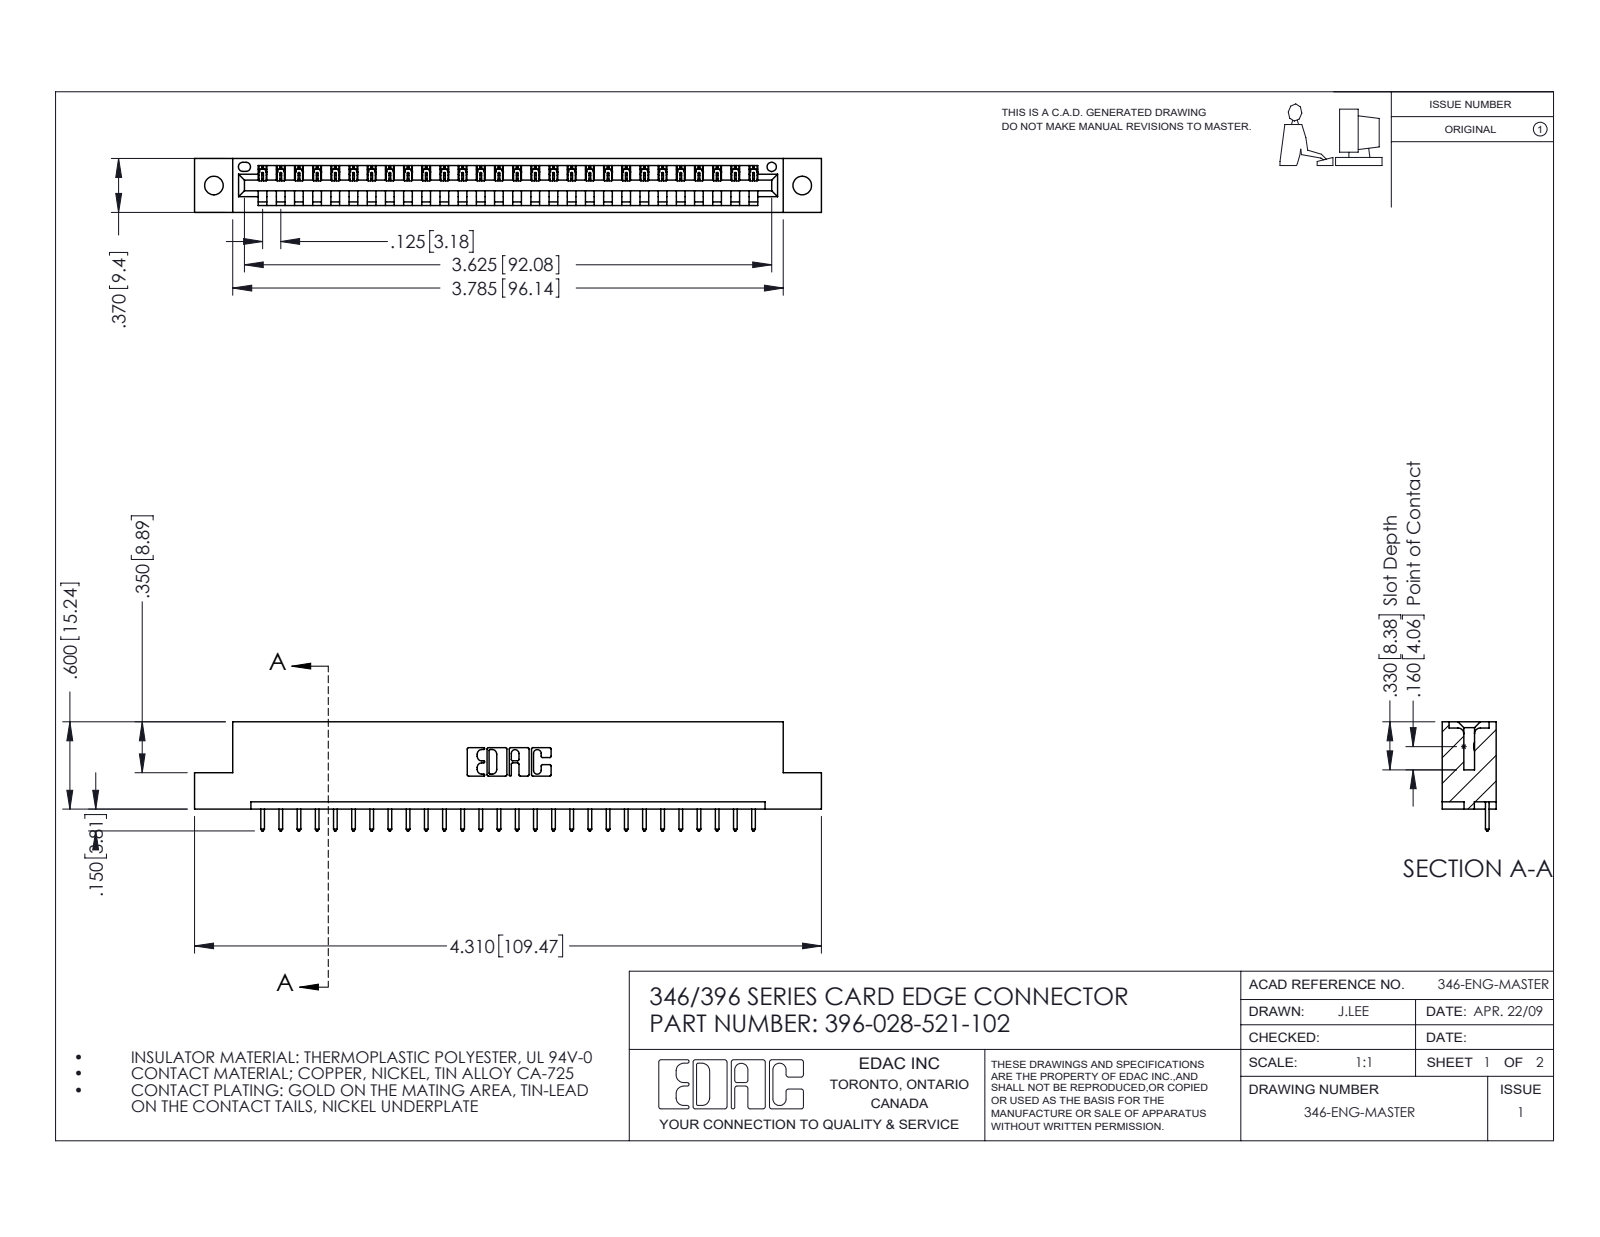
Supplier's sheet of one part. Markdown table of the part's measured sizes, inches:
| quantity | value |
| --- | --- |
| part name | 346 Part_Flush Mounting Lugs - 0.128 Dia; 396-028-521-102; 345-292-001_345-293-121 |
| STEP written by | SolidWorks 2016 (CONFIG_CONTROL_DESIGN) |
| units | inches |
| bodies | 29 solids, 1746 faces (1196 planar, 550 cylindrical, 0 other) |
| overall size | 4.31 × 0.75 × 0.37 |
| volume | 0.626 in³ |
| surface area | 18.74 in² |
| round holes (diameter × count) | 0.128 × 2, 0.064 × 1 |
| partial cylindrical surfaces (radius × count) | 0.006 × 56, 0.01 × 56, 0.01 × 22, 0.007 × 6, 0.031 × 6, 0.026 × 3, 0.031 × 2, 0.04 × 2 |
| main face-to-face distances | 0.048, 0.322, 0.37, 0.25, 0.072, 0.298, 0.025, 0.148, 0.222, 0.1 |
| hole center spacings | 0.246, 3.837, 4.045 |
